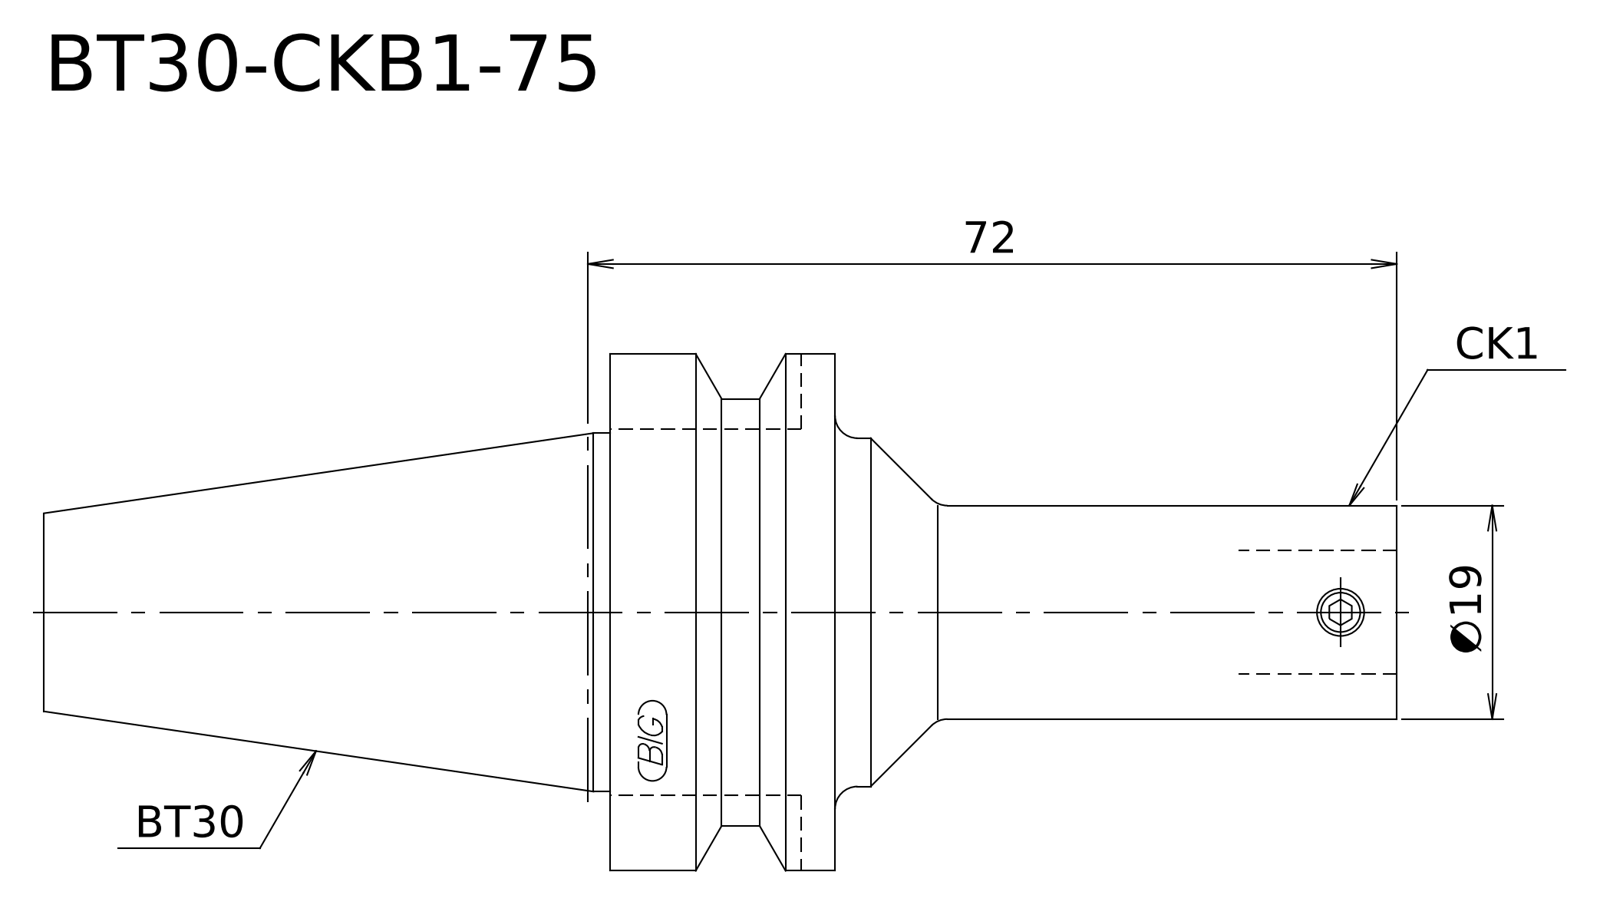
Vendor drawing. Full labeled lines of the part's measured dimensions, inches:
STEP written by: Kubotek KeyCreator V8.5.1 (14335) (CONFIG_CONTROL_DESIGN)
Units: inches
Bodies: 1 solid, 16 faces (4 planar, 6 cylindrical, 6 other)
Overall size (bounding box): 4.74 × 1.811 × 1.811
Volume: 4.466 in³ · Surface area: 20.12 in²
Round bosses / shafts (diameter × count): ⌀1.811 ×1, ⌀1.496 ×1, ⌀1.256 ×1, ⌀1.22 ×1, ⌀0.748 ×1
Main face-to-face distances: 0.787, 1.969, 2.756, 4.74, 2.772, 1.984
